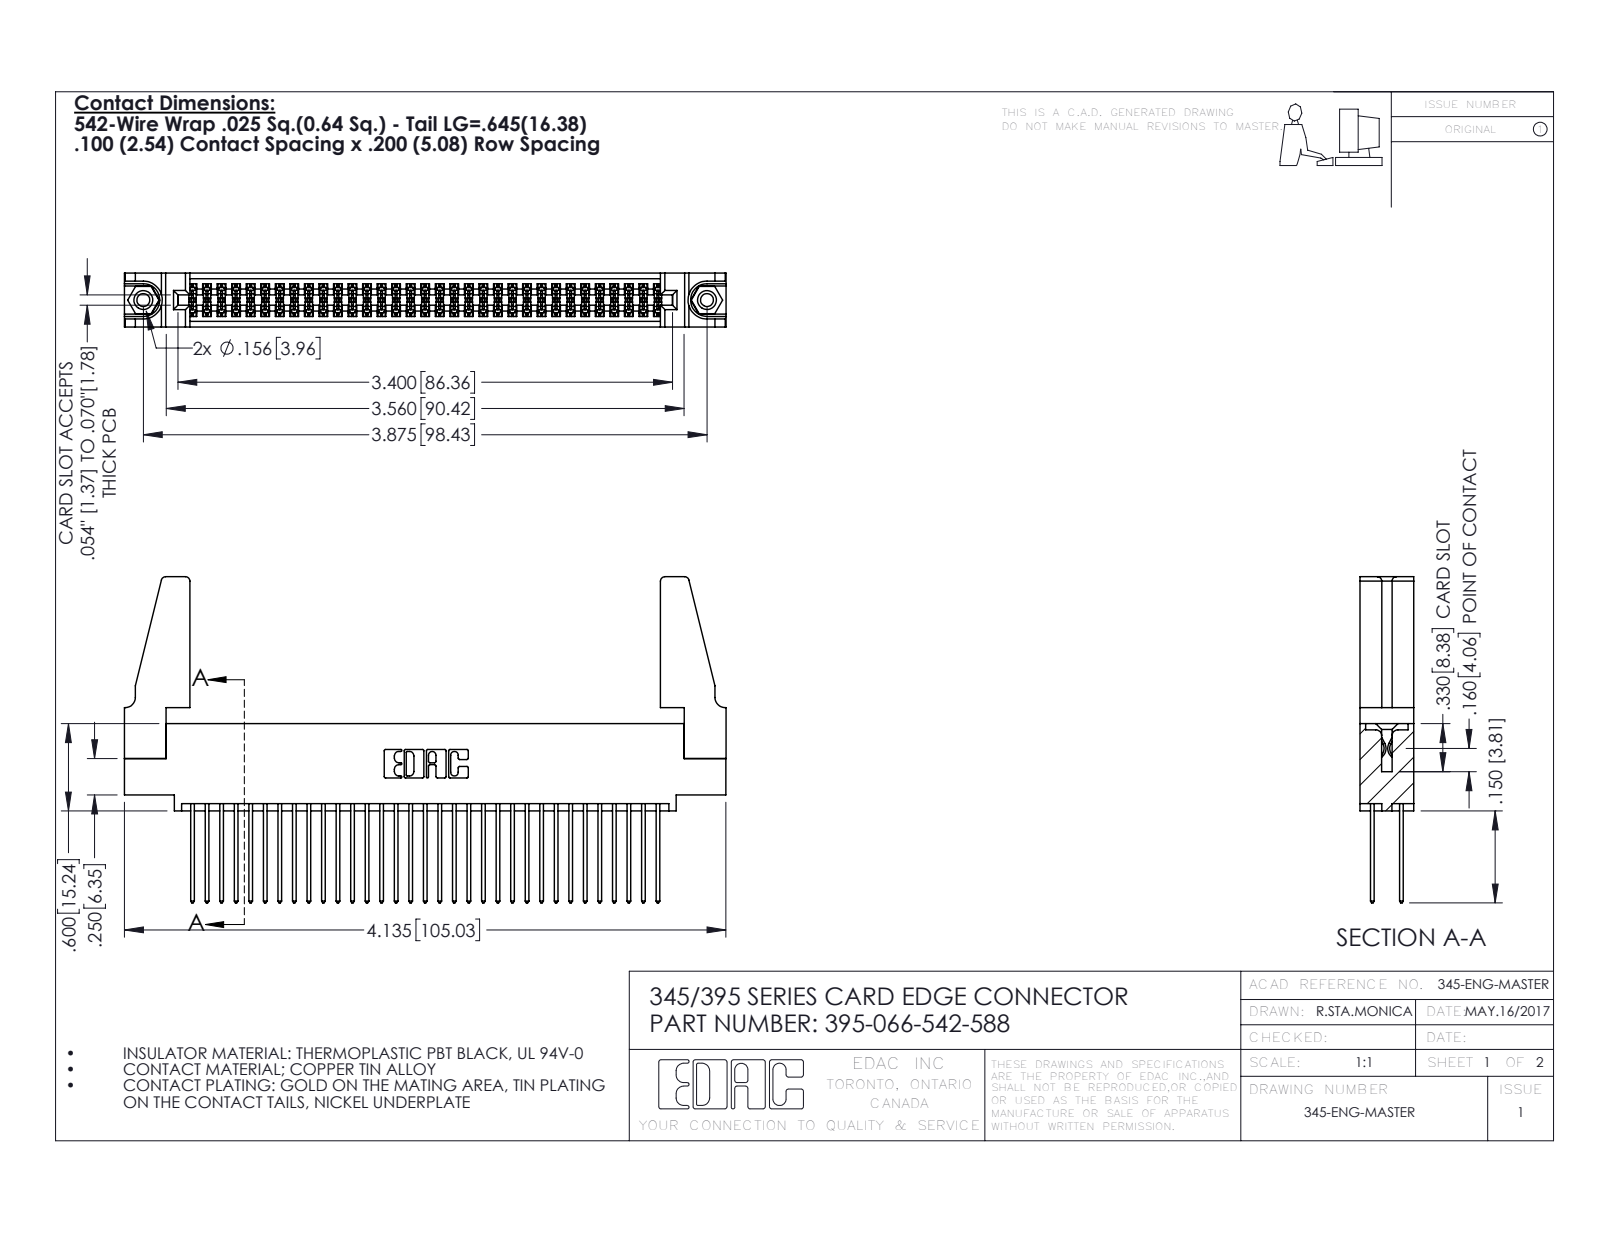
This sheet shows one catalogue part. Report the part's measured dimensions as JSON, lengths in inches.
{"part_name": "345-220-078_345-220-088; 395-066-542-588; 345-250-001_345-250-001-102; 345 Part_0.110 Offset - 0.156 Dia-TH (+1 more)", "step_written_by": "SolidWorks 2016 (CONFIG_CONTROL_DESIGN)", "units": "inches", "bodies": {"solids": 71, "faces": 3554, "planar": 2334, "cylindrical": 1204, "other": 16}, "overall_size": [4.136, 2.242, 0.37], "volume_in3": 0.83, "surface_area_in2": 30.67, "round_holes": [[0.089, 2], [0.125, 2], [0.156, 2], [0.064, 1]], "round_bosses_or_shafts": [[0.155, 2]], "partial_cylinders_radius": [[0.006, 99], [0.01, 66], [0.01, 22], [0.03, 8], [0.007, 6], [0.031, 6], [0.026, 3], [0.014, 2]], "face_to_face_distances": [0.072, 0.298, 0.2, 0.37, 0.098, 0.272, 0.025, 0.225, 0.175, 0.149], "hole_center_spacings": [0.27, 3.64, 3.875]}
